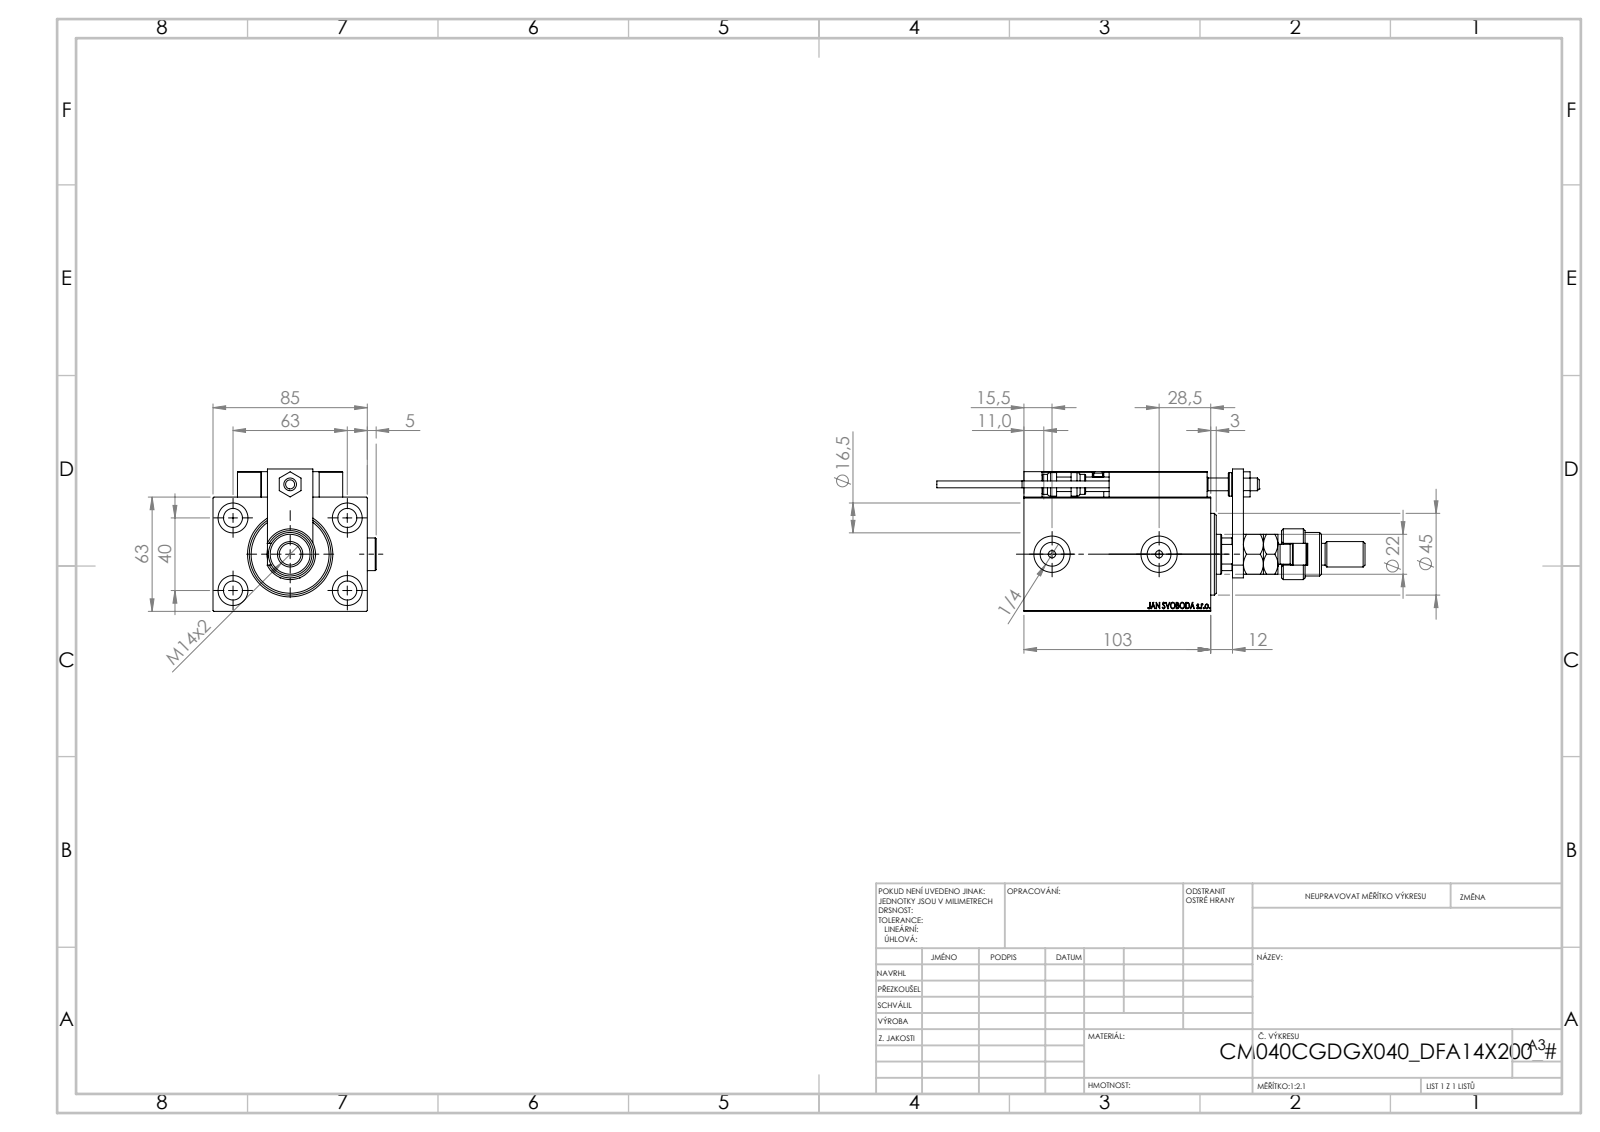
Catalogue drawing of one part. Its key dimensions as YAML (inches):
part_name: "ALLEN BOLT D8; MAGNET; MFA; SWITCH X (+8 more)"
step_written_by: "SolidWorks 2019 (CONFIG_CONTROL_DESIGN)"
units: inches
bodies: {solids: 27, faces: 1421, planar: 622, cylindrical: 217, other: 582}
overall_size: [9.291, 3.539, 3.091]
volume: 32.98
surface_area: 189.8
round_holes:
  - {diameter: 0.157, count: 6}
  - {diameter: 0.315, count: 5}
  - {diameter: 0.65, count: 5}
  - {diameter: 0.126, count: 4}
  - {diameter: 0.413, count: 4}
  - {diameter: 0.197, count: 2}
  - {diameter: 0.518, count: 2}
  - {diameter: 0.787, count: 2}
  - {diameter: 0.276, count: 1}
  - {diameter: 0.492, count: 1}
  - {diameter: 0.866, count: 1}
  - {diameter: 1.004, count: 1}
round_bosses_or_shafts:
  - {diameter: 0.709, count: 3}
  - {diameter: 0.433, count: 2}
  - {diameter: 0.197, count: 2}
  - {diameter: 0.15, count: 2}
  - {diameter: 1.102, count: 1}
  - {diameter: 0.945, count: 1}
  - {diameter: 0.551, count: 1}
  - {diameter: 0.512, count: 1}
partial_cylinders:
  - {radius: 0.012, count: 30}
  - {radius: 0.118, count: 2}
  - {radius: 0.384, count: 1}
  - {radius: 0.413, count: 1}
face_to_face_distances: [2.48, 0.472, 3.346, 3.583, 4.055, 0.551, 1.181, 0.709, 3.031, 0.236]
hole_center_spacings: [1.469, 0.448, 0.787, 1.165, 1.169, 1.42, 1.438, 1.575]
